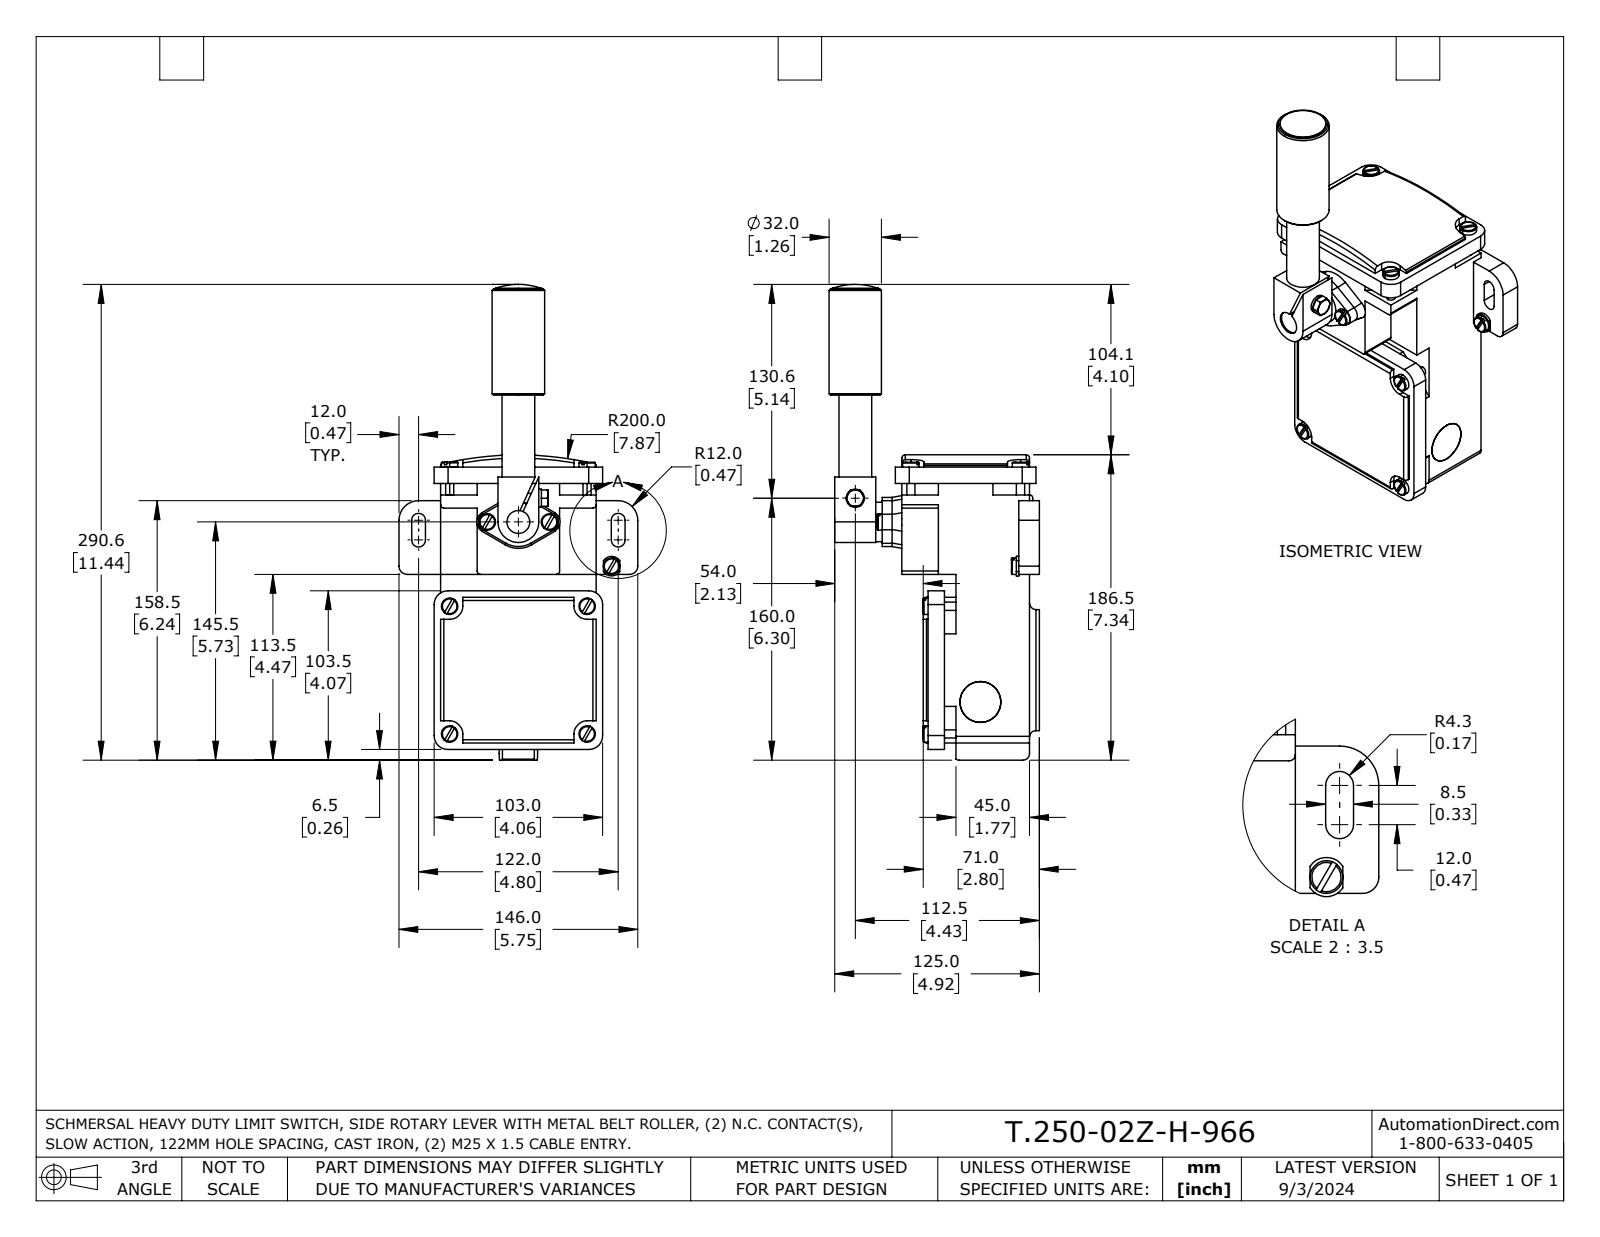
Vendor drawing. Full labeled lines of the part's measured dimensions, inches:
Part name (STEP PRODUCT): T.250-02Z-H-966
STEP written by: SolidWorks 2023 (AUTOMOTIVE_DESIGN)
Units: inches
Bodies: 4 solids, 372 faces (203 planar, 115 cylindrical, 54 other)
Overall size (bounding box): 11.441 × 5.748 × 5.059
Volume: 78.3 in³ · Surface area: 189.7 in²
Round holes (diameter × count): ⌀0.262 ×1, ⌀0.92 ×1
Round bosses / shafts (diameter × count): ⌀0.394 ×11, ⌀0.197 ×8, ⌀2.913 ×1, ⌀1.26 ×1, ⌀1.102 ×1, ⌀0.984 ×1, ⌀0.945 ×1, ⌀0.787 ×1
Partial cylindrical surfaces — rounded edges, fillets, slot ends (radius × count): R0.079 ×8, R0.315 ×8, R0.335 ×8, R0.157 ×4, R0.167 ×4, R0.039 ×2, R0.197 ×2, R0.217 ×2
Main face-to-face distances: 2.559, 3.74, 0.157, 0.236, 2.795, 0.512, 0.394, 0.787, 4.055, 2.185
Hole centre spacings: 5.753
